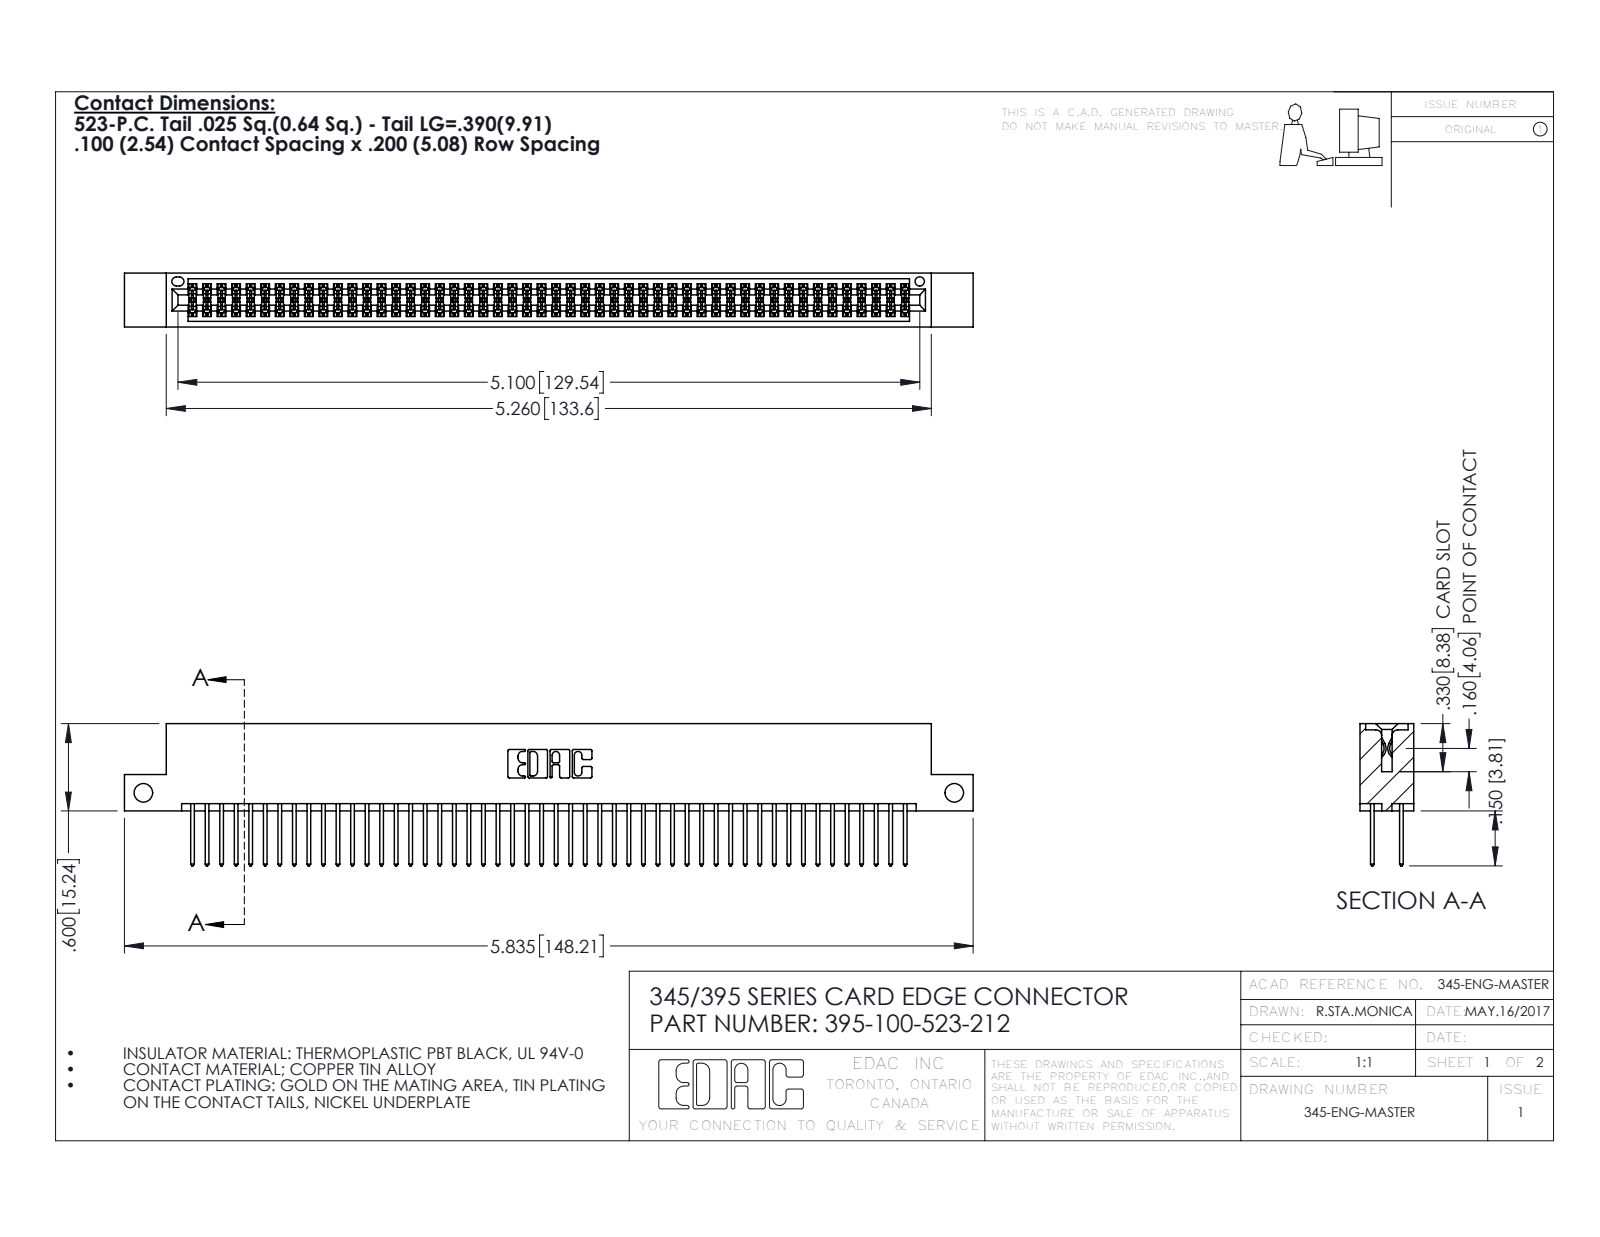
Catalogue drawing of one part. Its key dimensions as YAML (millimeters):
part_name: "395-100-523-212; 345 Part_Flush Mounting Lugs - Side Mount; 345-292-001_345-293-123"
step_written_by: "SolidWorks 2016 (CONFIG_CONTROL_DESIGN)"
units: millimeters
bodies: {solids: 101, faces: 5126, planar: 3380, cylindrical: 1746, other: 0}
overall_size: [148.2, 24.8, 9.4]
volume: 14600
surface_area: 22500
round_holes:
  - {diameter: 3.3, count: 2}
  - {diameter: 1.6, count: 1}
partial_cylinders:
  - {radius: 0.2, count: 150}
  - {radius: 0.3, count: 100}
  - {radius: 0.3, count: 22}
  - {radius: 0.2, count: 6}
  - {radius: 0.8, count: 6}
  - {radius: 0.7, count: 3}
  - {radius: 0.4, count: 2}
  - {radius: 0.5, count: 2}
face_to_face_distances: [7.6, 1.8, 5.1, 2.5, 6.9, 0.6, 9.4, 5.7, 4.4, 3.8]
hole_center_spacings: [141.6]
